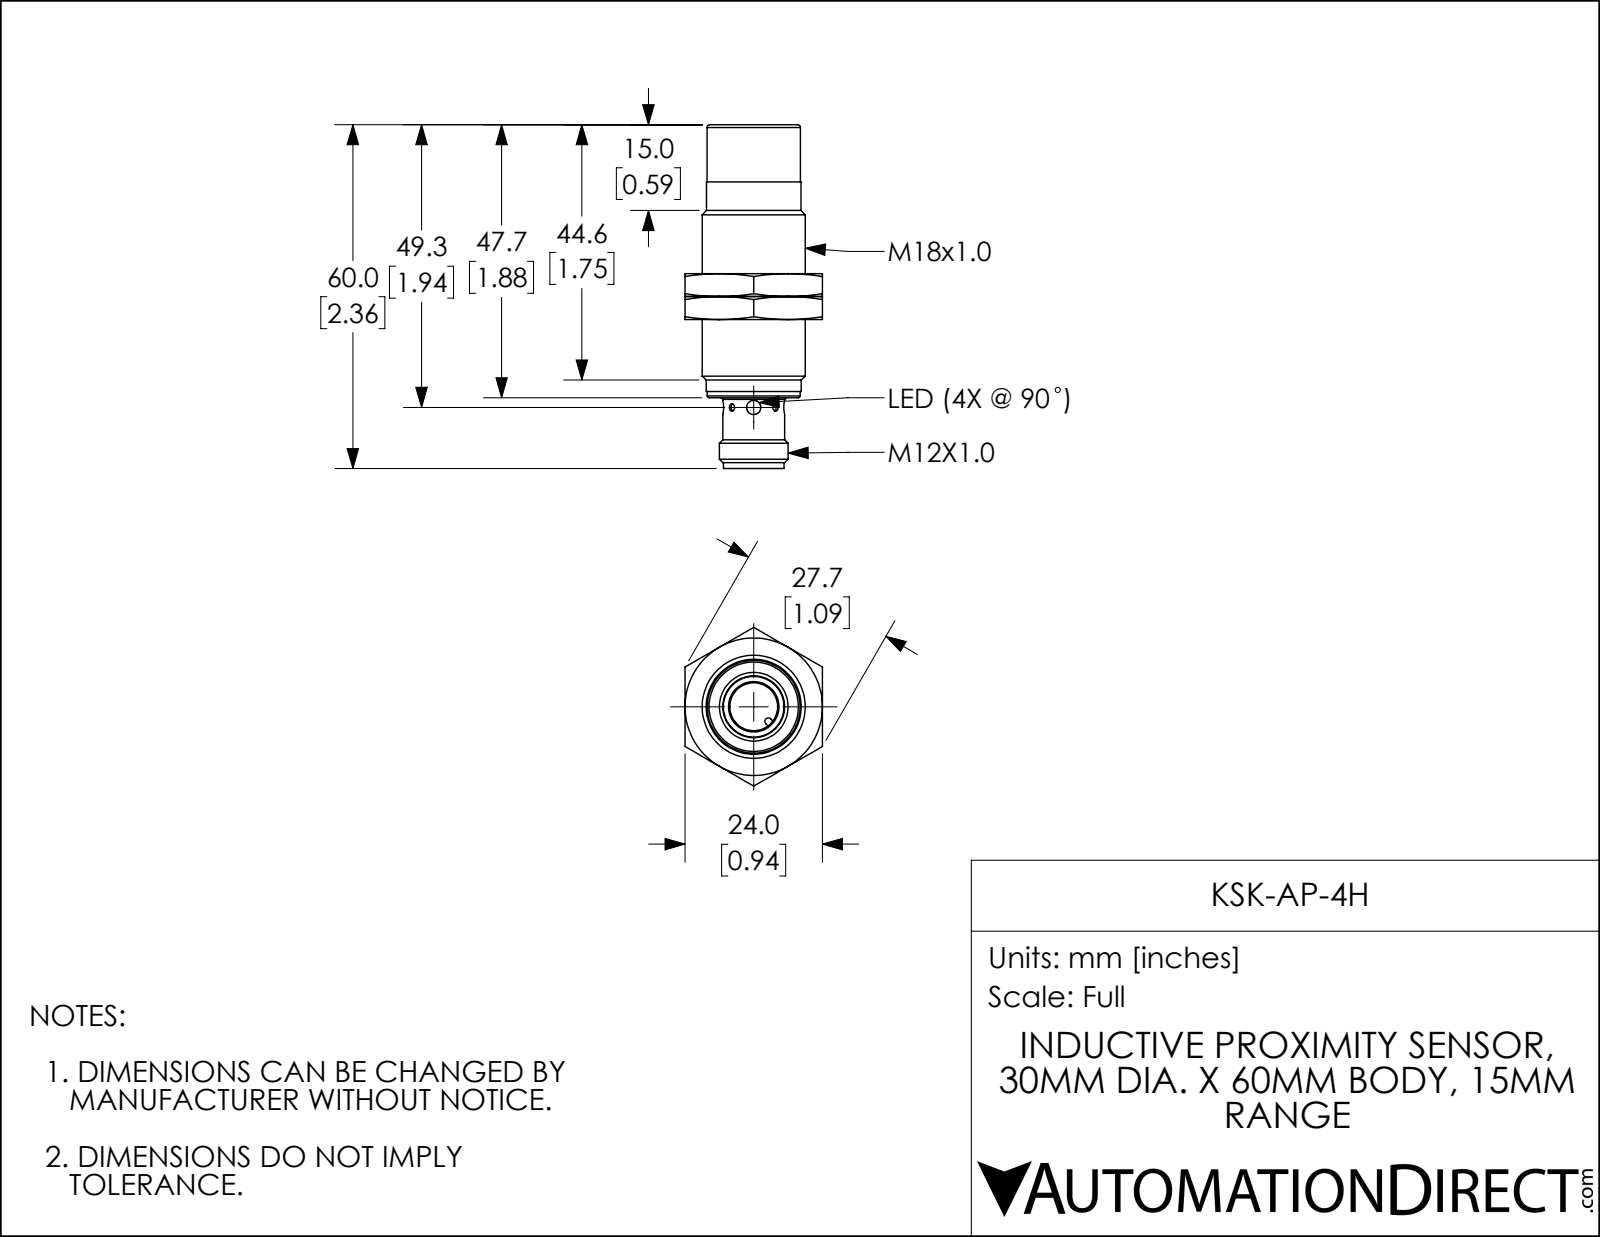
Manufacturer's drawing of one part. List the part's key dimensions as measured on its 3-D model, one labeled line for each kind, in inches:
Part name (STEP PRODUCT): KSK-AP-4H
STEP written by: SolidWorks 2017 (AUTOMOTIVE_DESIGN)
Units: inches
Bodies: 1 solid, 83 faces (24 planar, 19 cylindrical, 40 other)
Overall size (bounding box): 2.362 × 1.091 × 0.945
Volume: 0.851 in³ · Surface area: 6.974 in²
Round holes (diameter × count): ⌀0.329 ×1
Round bosses / shafts (diameter × count): ⌀0.709 ×1, ⌀0.654 ×1, ⌀0.65 ×1, ⌀0.642 ×1, ⌀0.638 ×1, ⌀0.472 ×1, ⌀0.425 ×1, ⌀0.417 ×1
Partial cylindrical surfaces — rounded edges, fillets, slot ends (radius × count): R0.213 ×8, R0.024 ×1
Main face-to-face distances: 0.945, 1.024, 1.339, 0.315, 0.537, 0.852, 1.876, 0.136, 0.673, 0.988
